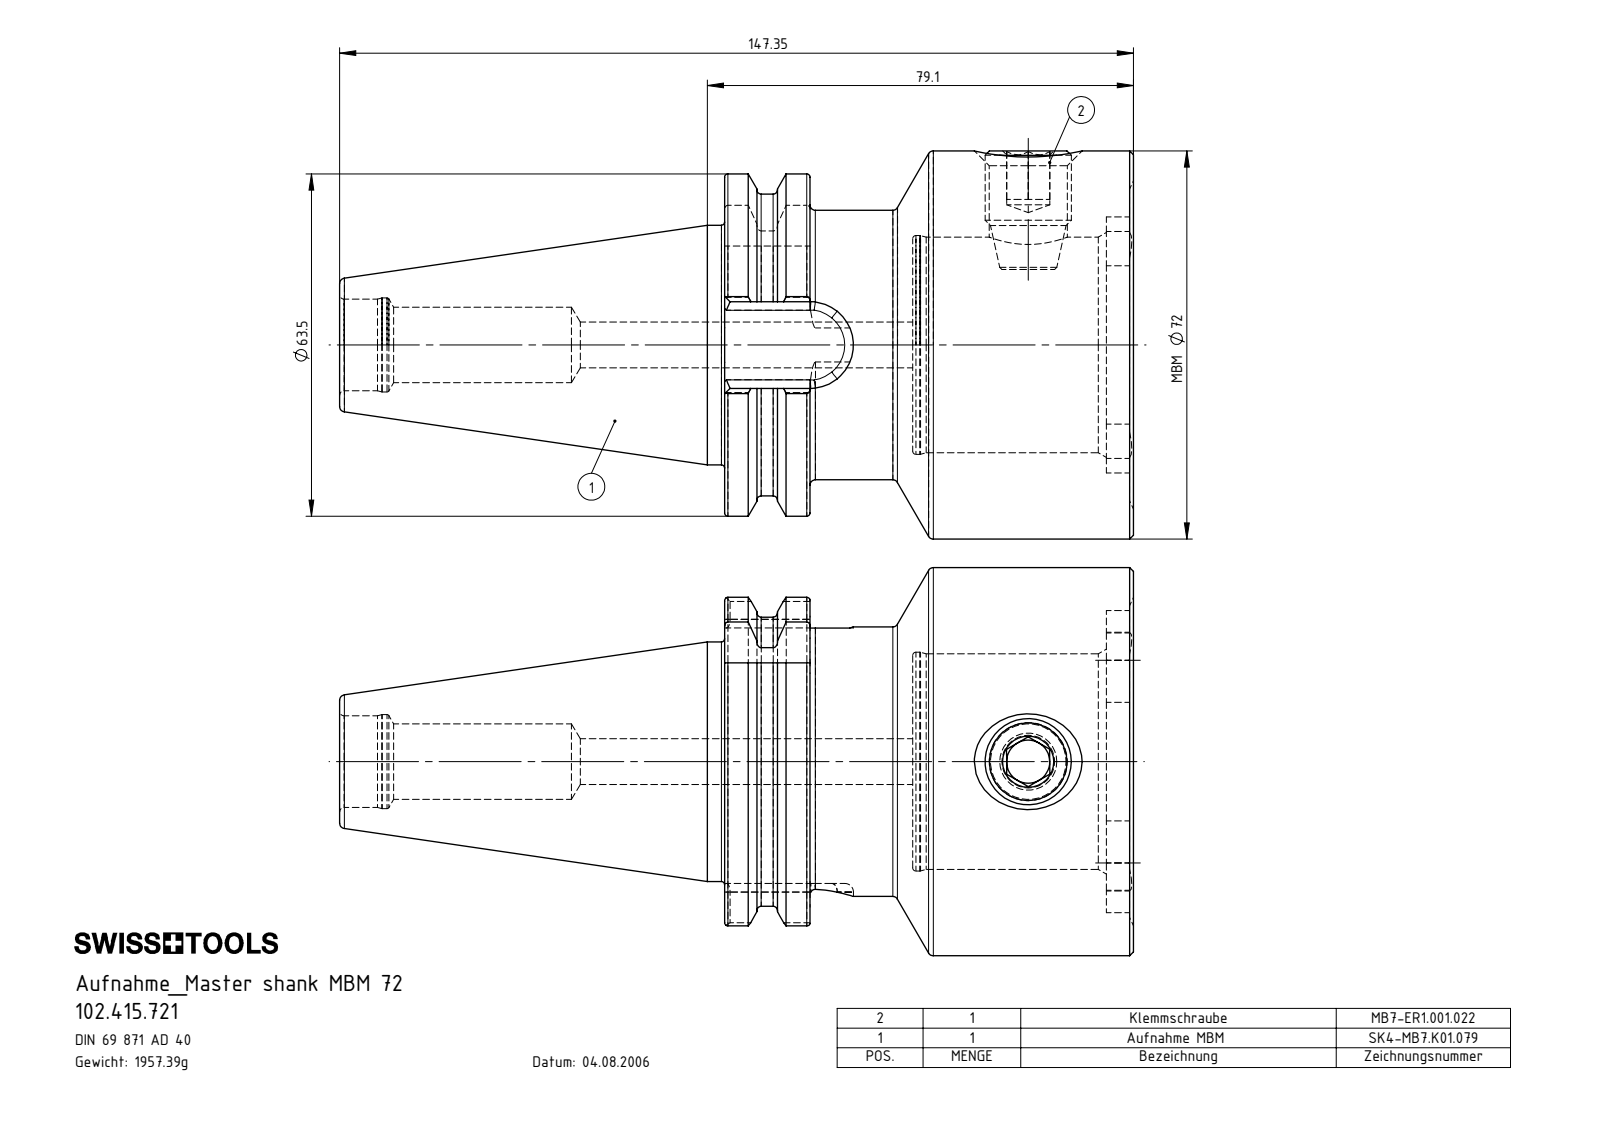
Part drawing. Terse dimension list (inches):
name: SK4-MB7.K01.079_C; 102.415.721; MB7-ER1.001.022_A
written by: SolidWorks 2017 (CONFIG_CONTROL_DESIGN)
unit: in
bodies: 2 solids, 192 faces (57 planar, 58 cylindrical, 77 other)
size: 5.801 × 2.835 × 2.835
volume: 15.22 in³; area: 66.05 in²
holes: 1× ⌀0.315, 1× ⌀0.335, 1× ⌀0.551, 1× ⌀0.571, 1× ⌀0.669, 1× ⌀0.687, 1× ⌀1.575, 1× ⌀1.598
bosses: 1× ⌀2.835, 1× ⌀1.969, 1× ⌀1.75, 1× ⌀0.63
rounds: 8× R0.063, 4× R0.205, 1× R0.315, 1× R0.317, 1× R0.935, 1× R1.102, 1× R1.103, 1× R1.25
face distances: 1.374, 2.988, 1.614, 2.789, 1.415, 0.199, 0.624, 0.75, 2.165, 2.364
